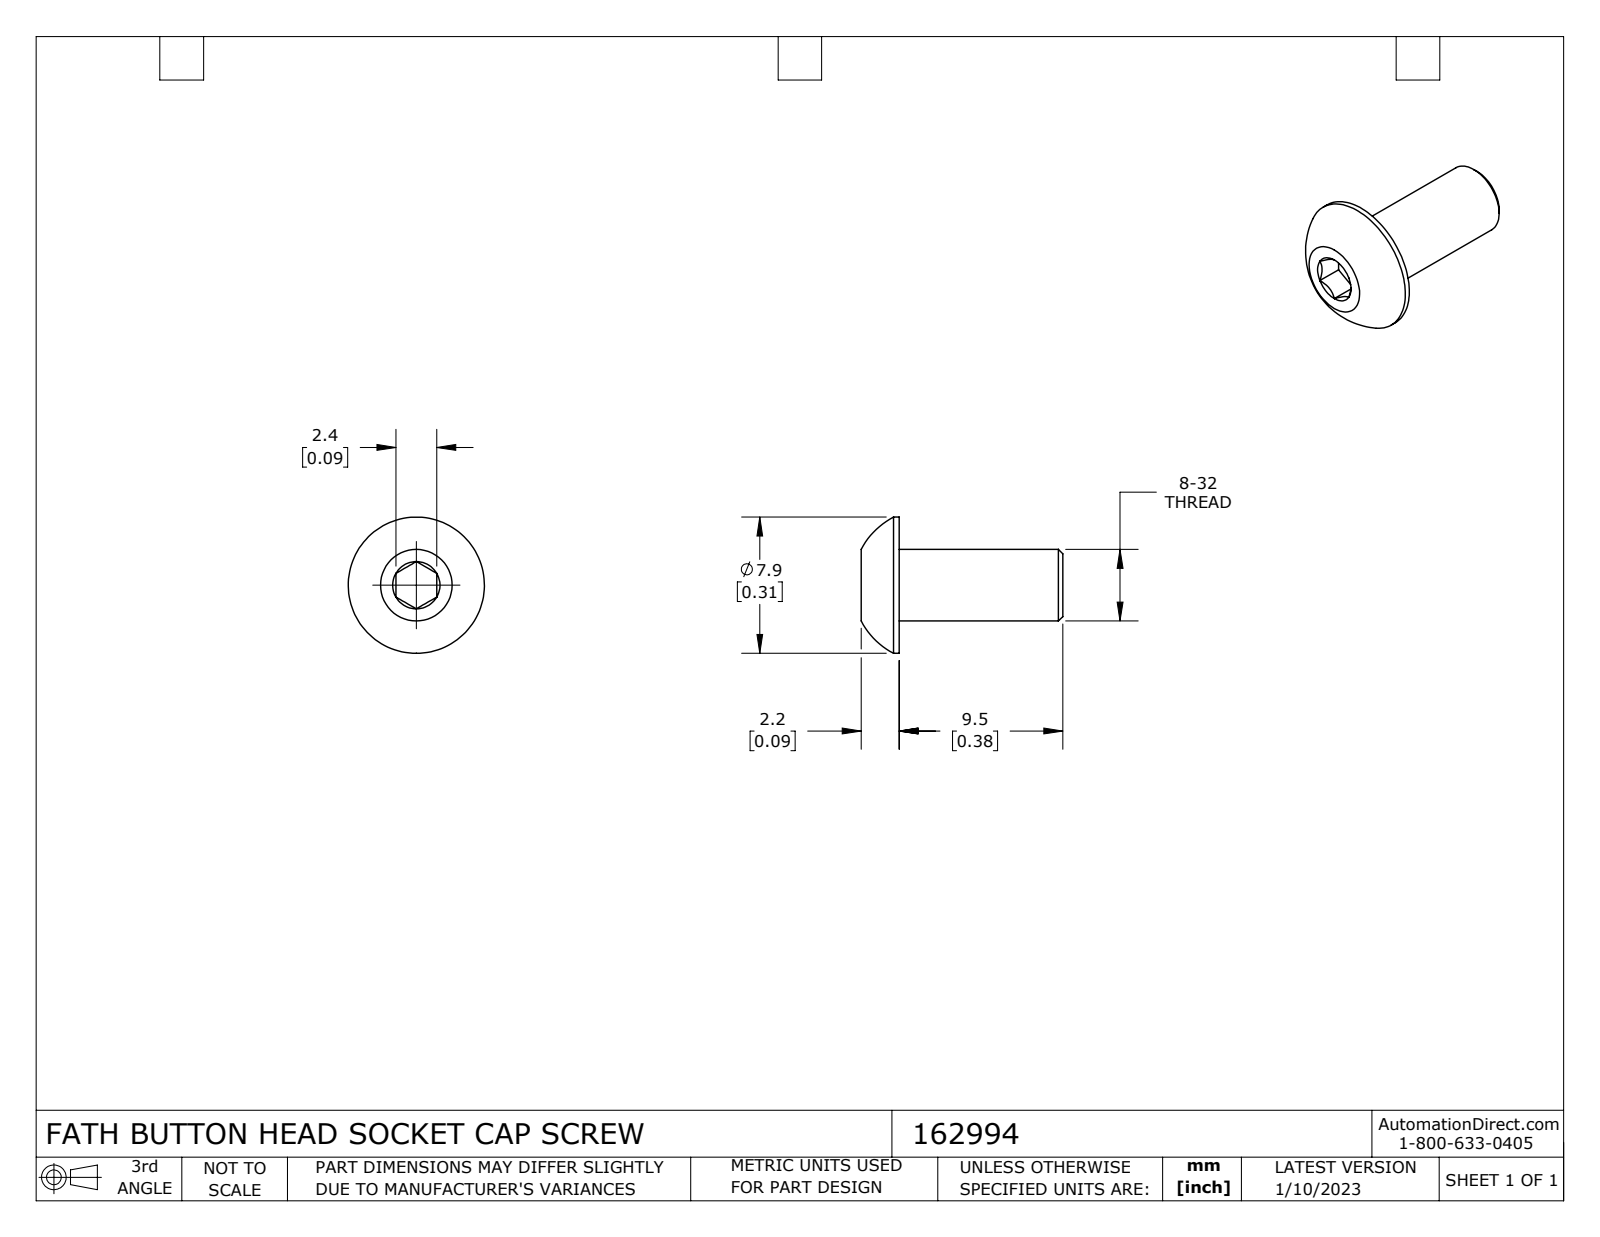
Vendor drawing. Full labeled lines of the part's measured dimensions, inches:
Part name (STEP PRODUCT): 162994
STEP written by: SolidWorks 2021 (CONFIG_CONTROL_DESIGN)
Units: inches
Bodies: 1 solid, 28 faces (12 planar, 4 cylindrical, 12 other)
Overall size (bounding box): 0.462 × 0.312 × 0.312
Volume: 0.012 in³ · Surface area: 0.403 in²
Round bosses / shafts (diameter × count): ⌀0.312 ×1, ⌀0.164 ×1
Main face-to-face distances: 0.375, 0.462, 0.087, 0.094, 0.401, 0.026, 0.061, 0.047
